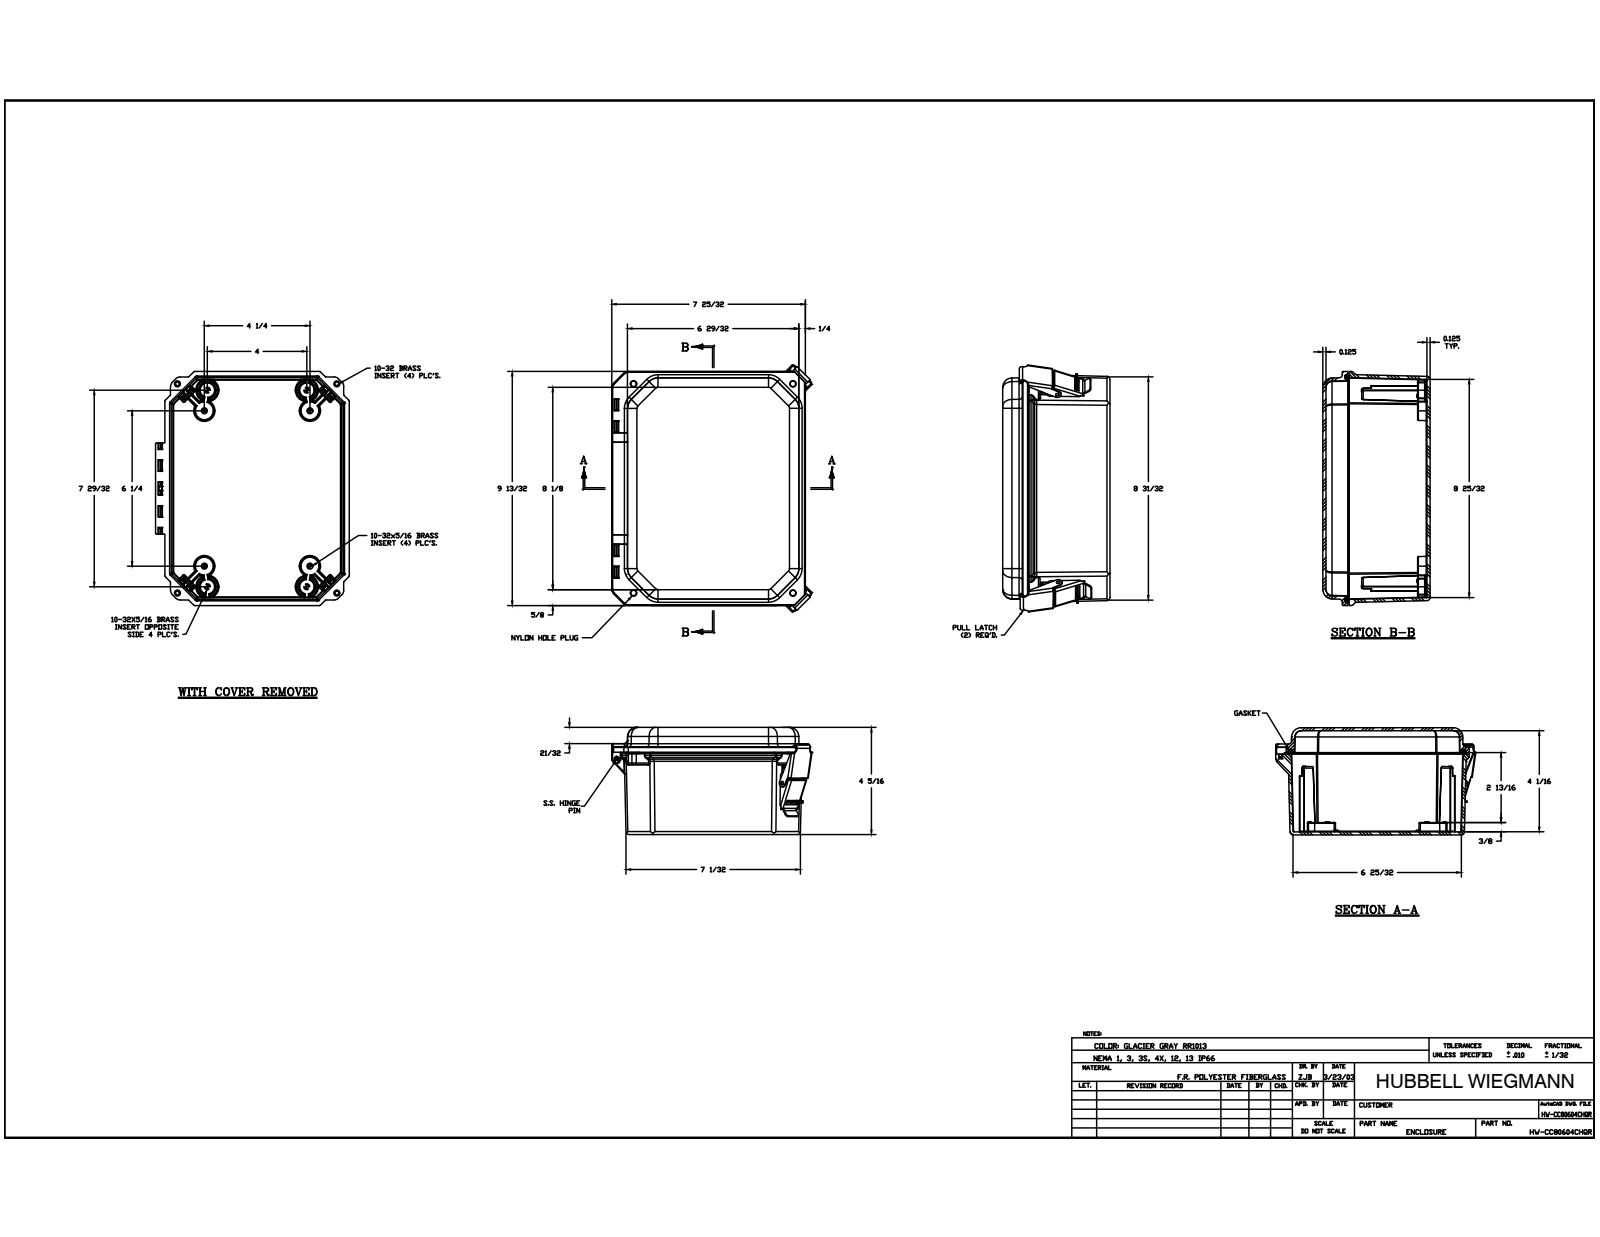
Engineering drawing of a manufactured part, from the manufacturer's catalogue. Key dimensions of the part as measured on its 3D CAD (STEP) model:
Part name (STEP PRODUCT): DS080604BOX; GA806; DSCC080604CVR; WP806HLU (+6 more)
STEP written by: Autodesk Inventor 2014 (AUTOMOTIVE_DESIGN)
Units: millimetres
Bodies: 29 solids, 2169 faces (656 planar, 841 cylindrical, 672 other)
Overall size (bounding box): 255.14 × 205.94 × 109.53
Volume: 631 386 mm³ · Surface area: 390 237 mm²
Round holes (diameter × count): ⌀3.96 ×12, ⌀3.43 ×8, ⌀3.86 ×8, ⌀3.81 ×4, ⌀5.56 ×4, ⌀6.4 ×4, ⌀7.92 ×4, ⌀3.43 ×2, ⌀9.52 ×2, ⌀3.48 ×1
Round bosses / shafts (diameter × count): ⌀6.25 ×12, ⌀22.1 ×4, ⌀7.62 ×4, ⌀5.3 ×4, ⌀3.43 ×3
Partial cylindrical surfaces — rounded edges, fillets, slot ends (radius × count): R0.25 ×135, R0.13 ×94, R0.51 ×67, R0.76 ×56, R3.17 ×29, R2.29 ×26, R0.76 ×24, R1.52 ×24
Main face-to-face distances: 3.17, 106.35, 109.52, 103.18, 3.15, 89.69, 16.66, 1.27, 25.4, 22.23
Hole centre spacings: 6.35, 188.25, 208.09, 230.26, 21.27, 38.85, 106.86, 138.16
